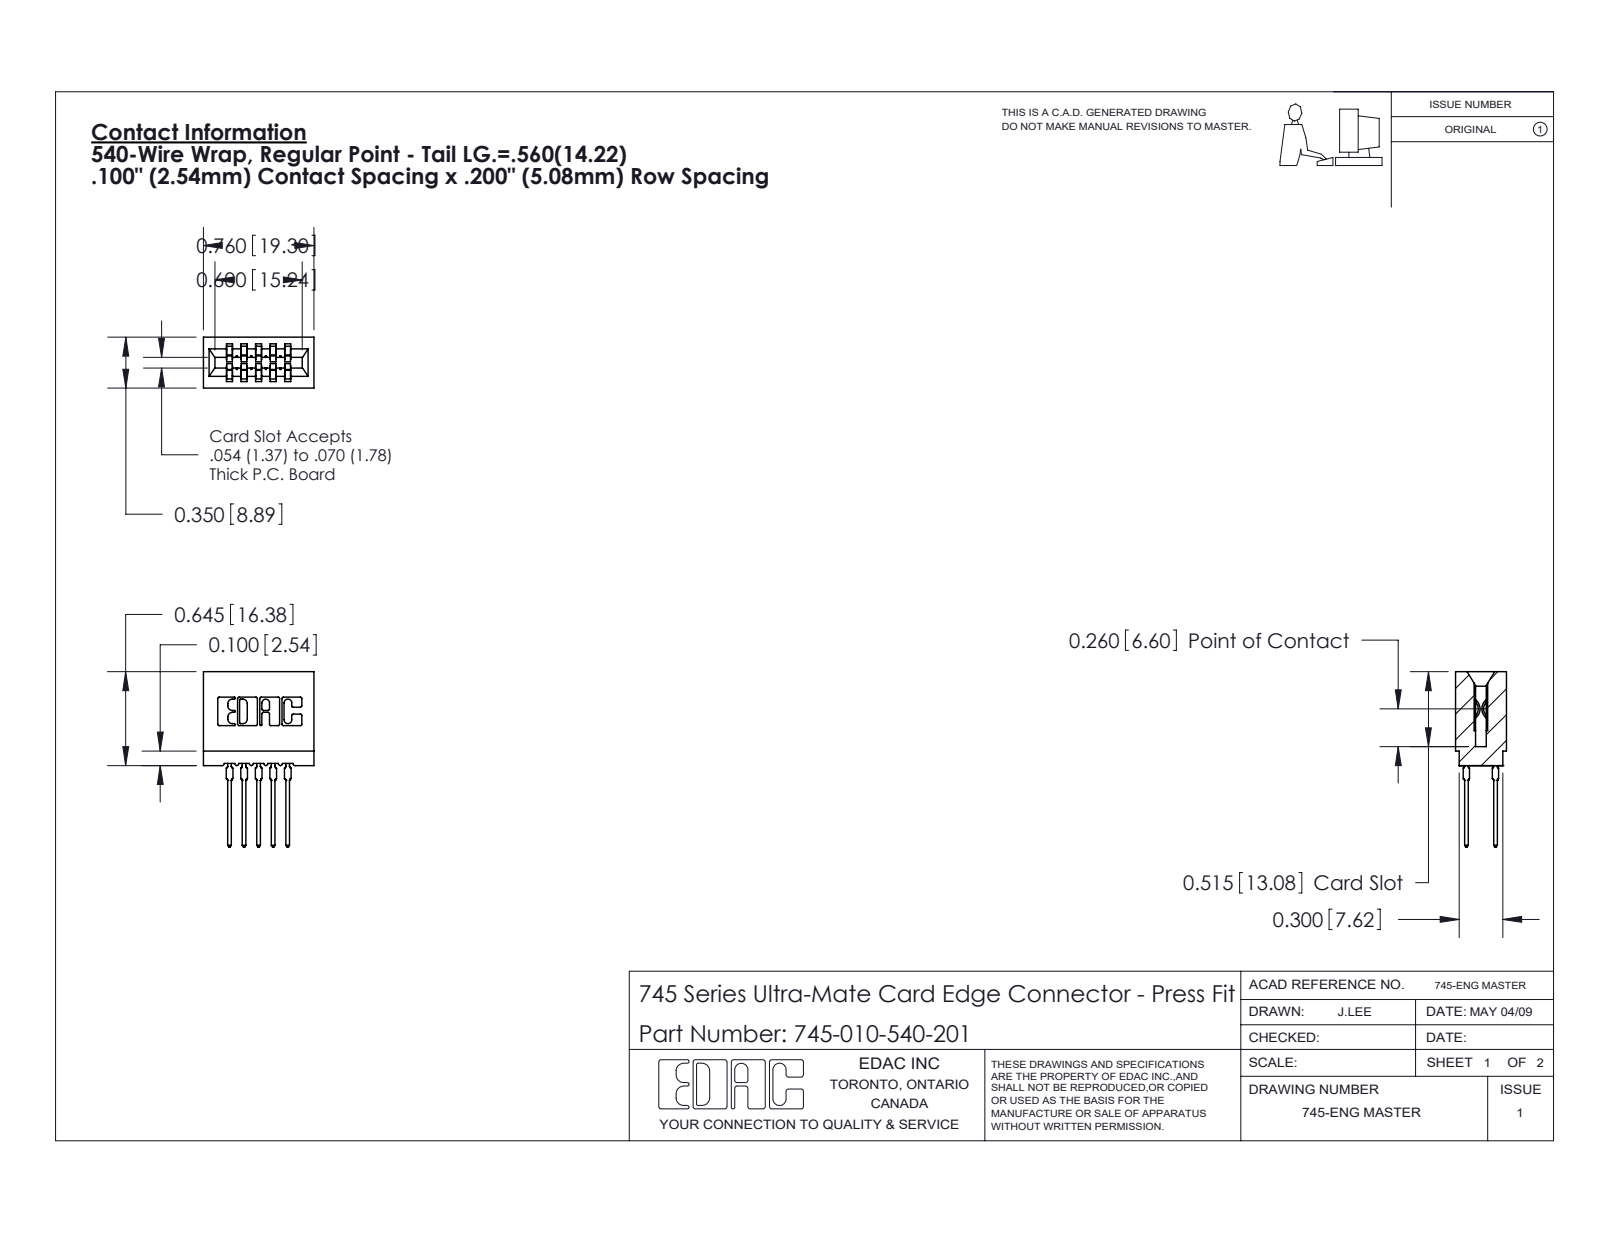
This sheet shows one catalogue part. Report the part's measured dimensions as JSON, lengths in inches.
{"part_name": "745-010-540-201; 745 Part_Insulator Option - 01; 745-292-001_540", "step_written_by": "SolidWorks 2020 (CONFIG_CONTROL_DESIGN)", "units": "inches", "bodies": {"solids": 11, "faces": 990, "planar": 515, "cylindrical": 215, "other": 260}, "overall_size": [1.206, 0.76, 0.35], "volume_in3": 0.122, "surface_area_in2": 5.127, "partial_cylinders_radius": [[0.01, 22], [0.021, 20], [0.015, 10], [0.005, 8], [0.011, 8], [0.007, 6], [0.031, 6], [0.026, 3]], "face_to_face_distances": [0.1, 0.2, 0.042, 0.142, 0.3, 0.058, 0.287, 0.35, 0.242, 0.158]}
